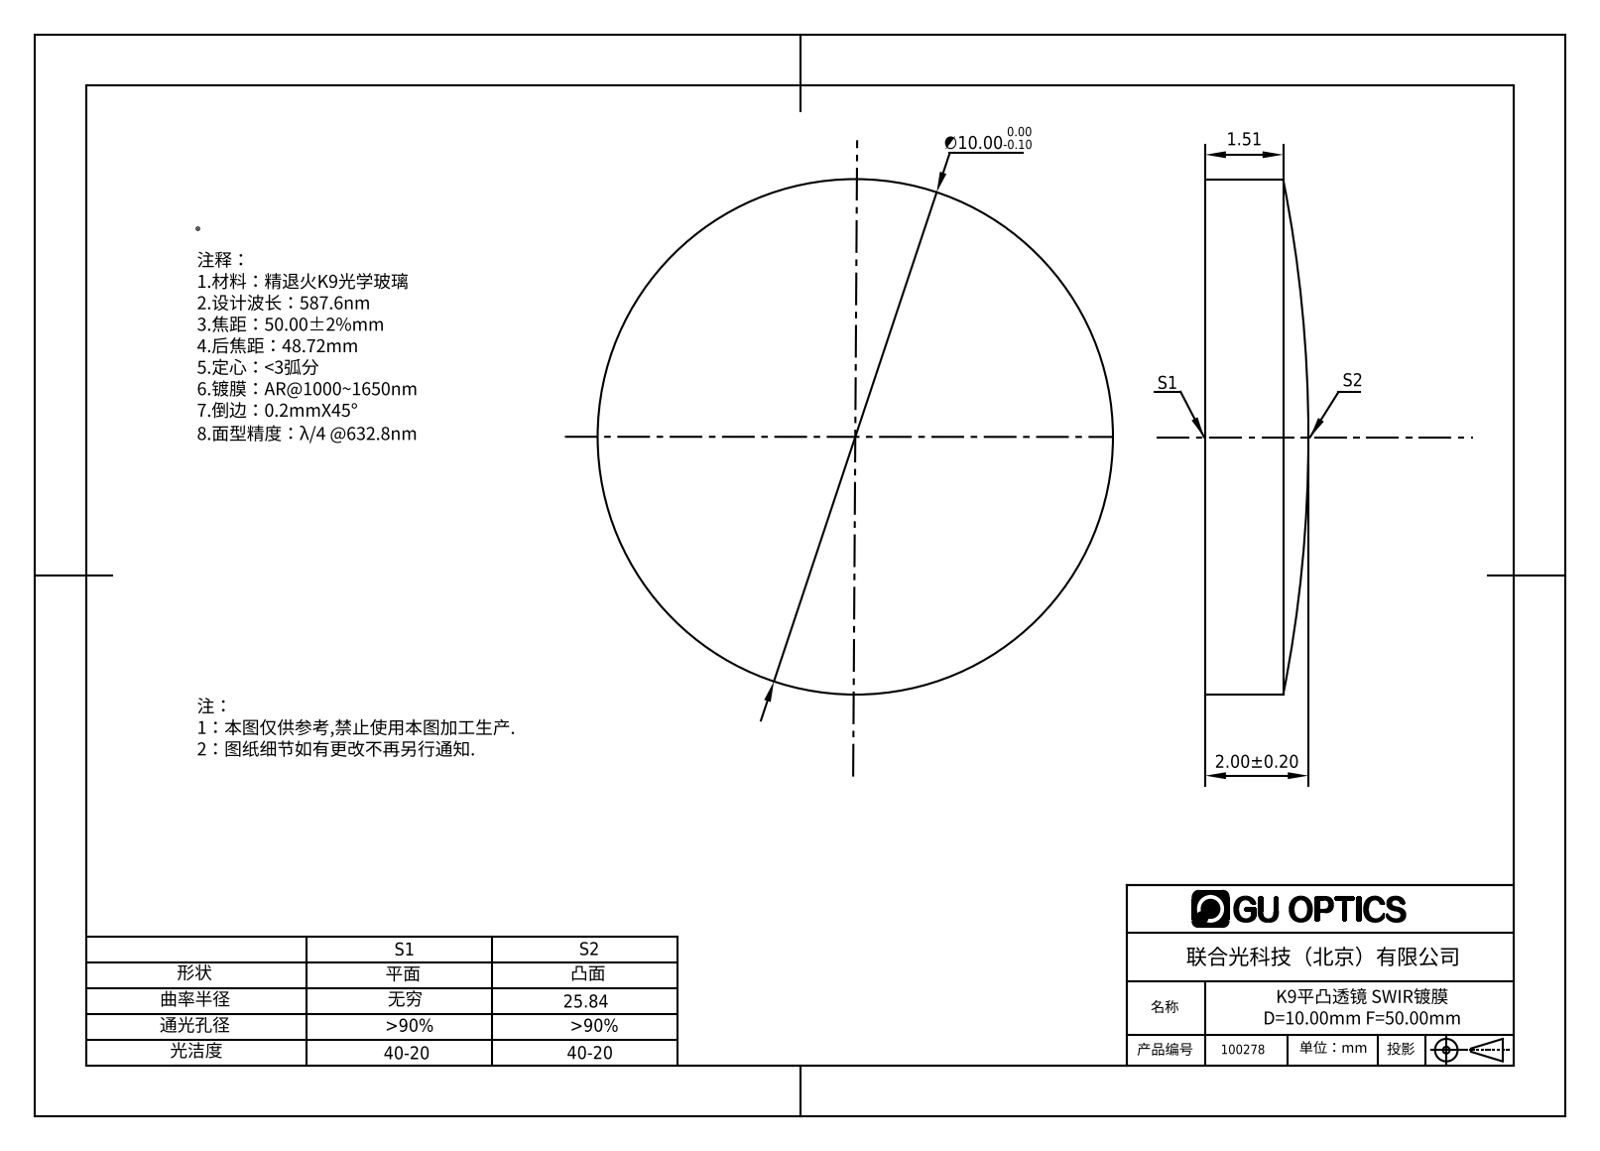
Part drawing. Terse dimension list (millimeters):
name: 100106
written by: SolidWorks 2016 (AUTOMOTIVE_DESIGN)
unit: mm
bodies: 1 solid, 5 faces (1 planar, 2 cylindrical, 2 other)
size: 1 × 1 × 0.2
volume: 0.138 mm³; area: 2 mm²
bosses: 1× ⌀1
